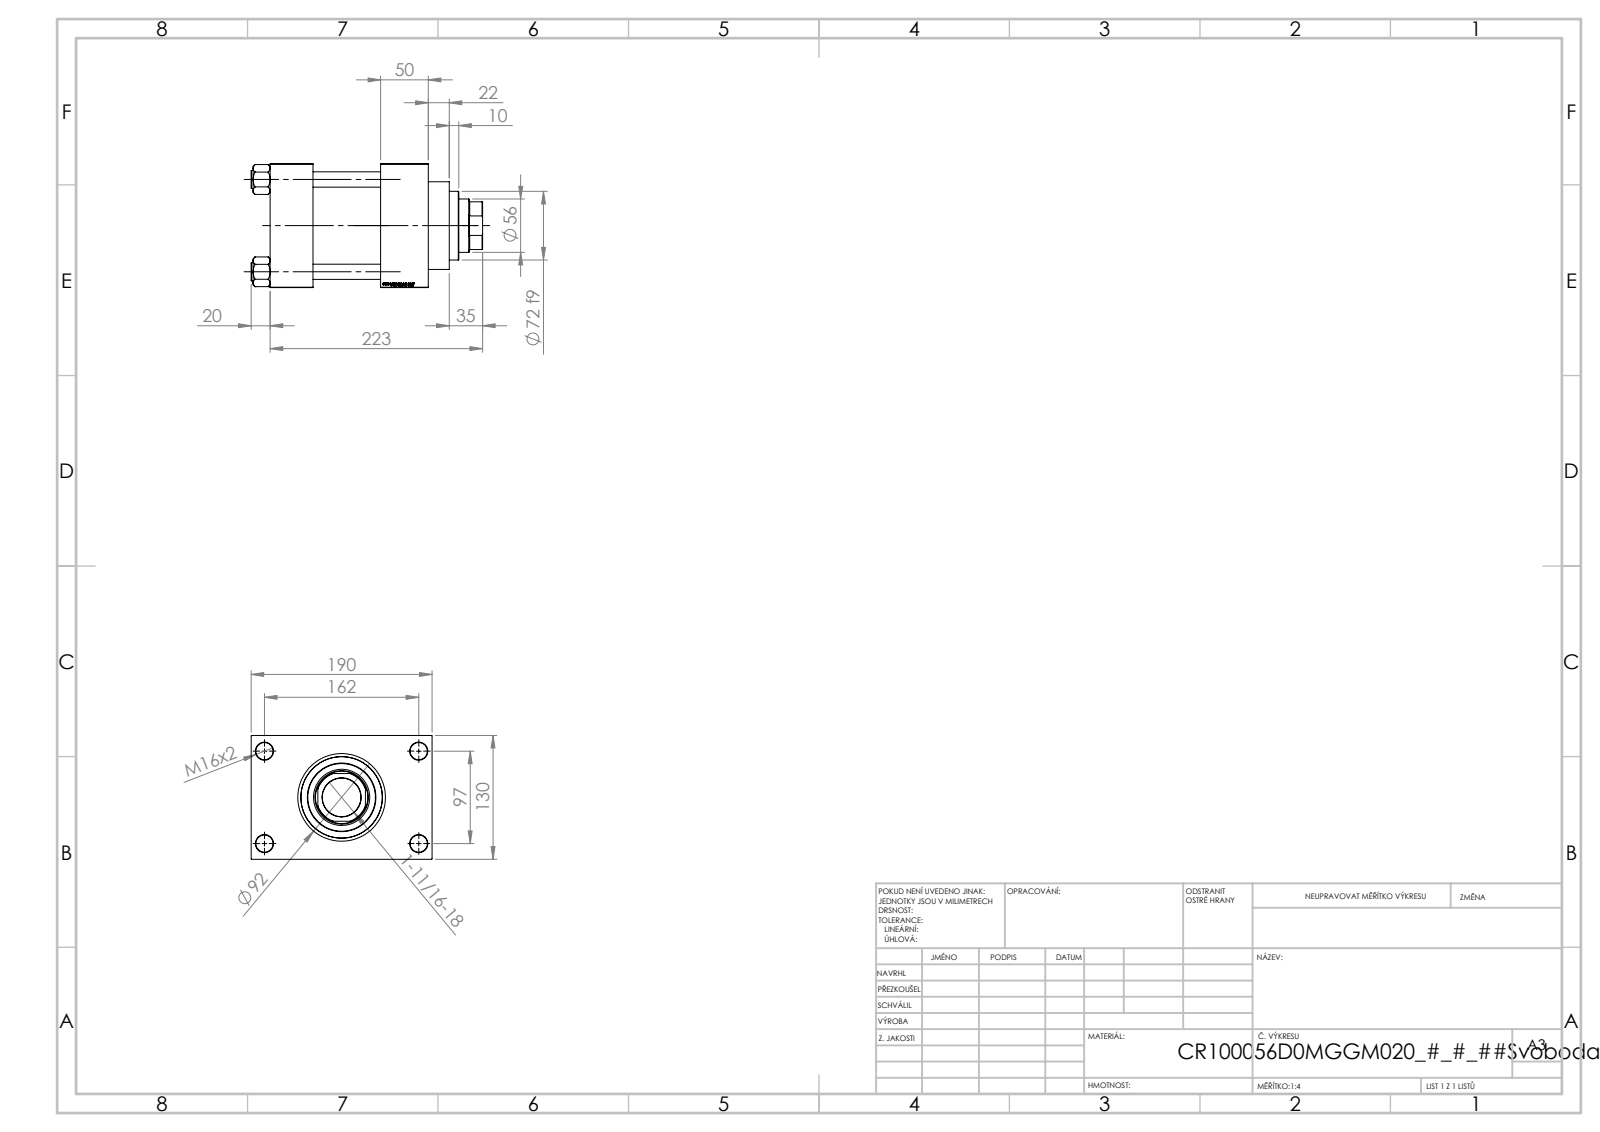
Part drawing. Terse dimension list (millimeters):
name: V215CR_D_TYCINKA; V215CR_D_Body; V215CR_VCP_D; NUT_M5_D (+1 more)
written by: SolidWorks 2019 (CONFIG_CONTROL_DESIGN)
unit: mm
bodies: 11 solids, 1152 faces (545 planar, 89 cylindrical, 518 other)
size: 243 × 190 × 130
volume: 2 644 000 mm³; area: 359 880 mm²
holes: 4× ⌀16, 4× ⌀18, 2× ⌀7, 2× ⌀26.44, 2× ⌀35, 1× ⌀40.5, 1× ⌀56, 1× ⌀59, 1× ⌀76, 1× ⌀85.5, 1× ⌀100
bosses: 4× ⌀19, 1× ⌀106, 1× ⌀92, 1× ⌀72
rounds: 1× R27
face distances: 130, 116, 50, 45, 71, 166, 121, 30, 160, 190
hole spacings: 32.55, 68.52, 94.41, 96.9, 102.27, 129.45, 161.73, 97
